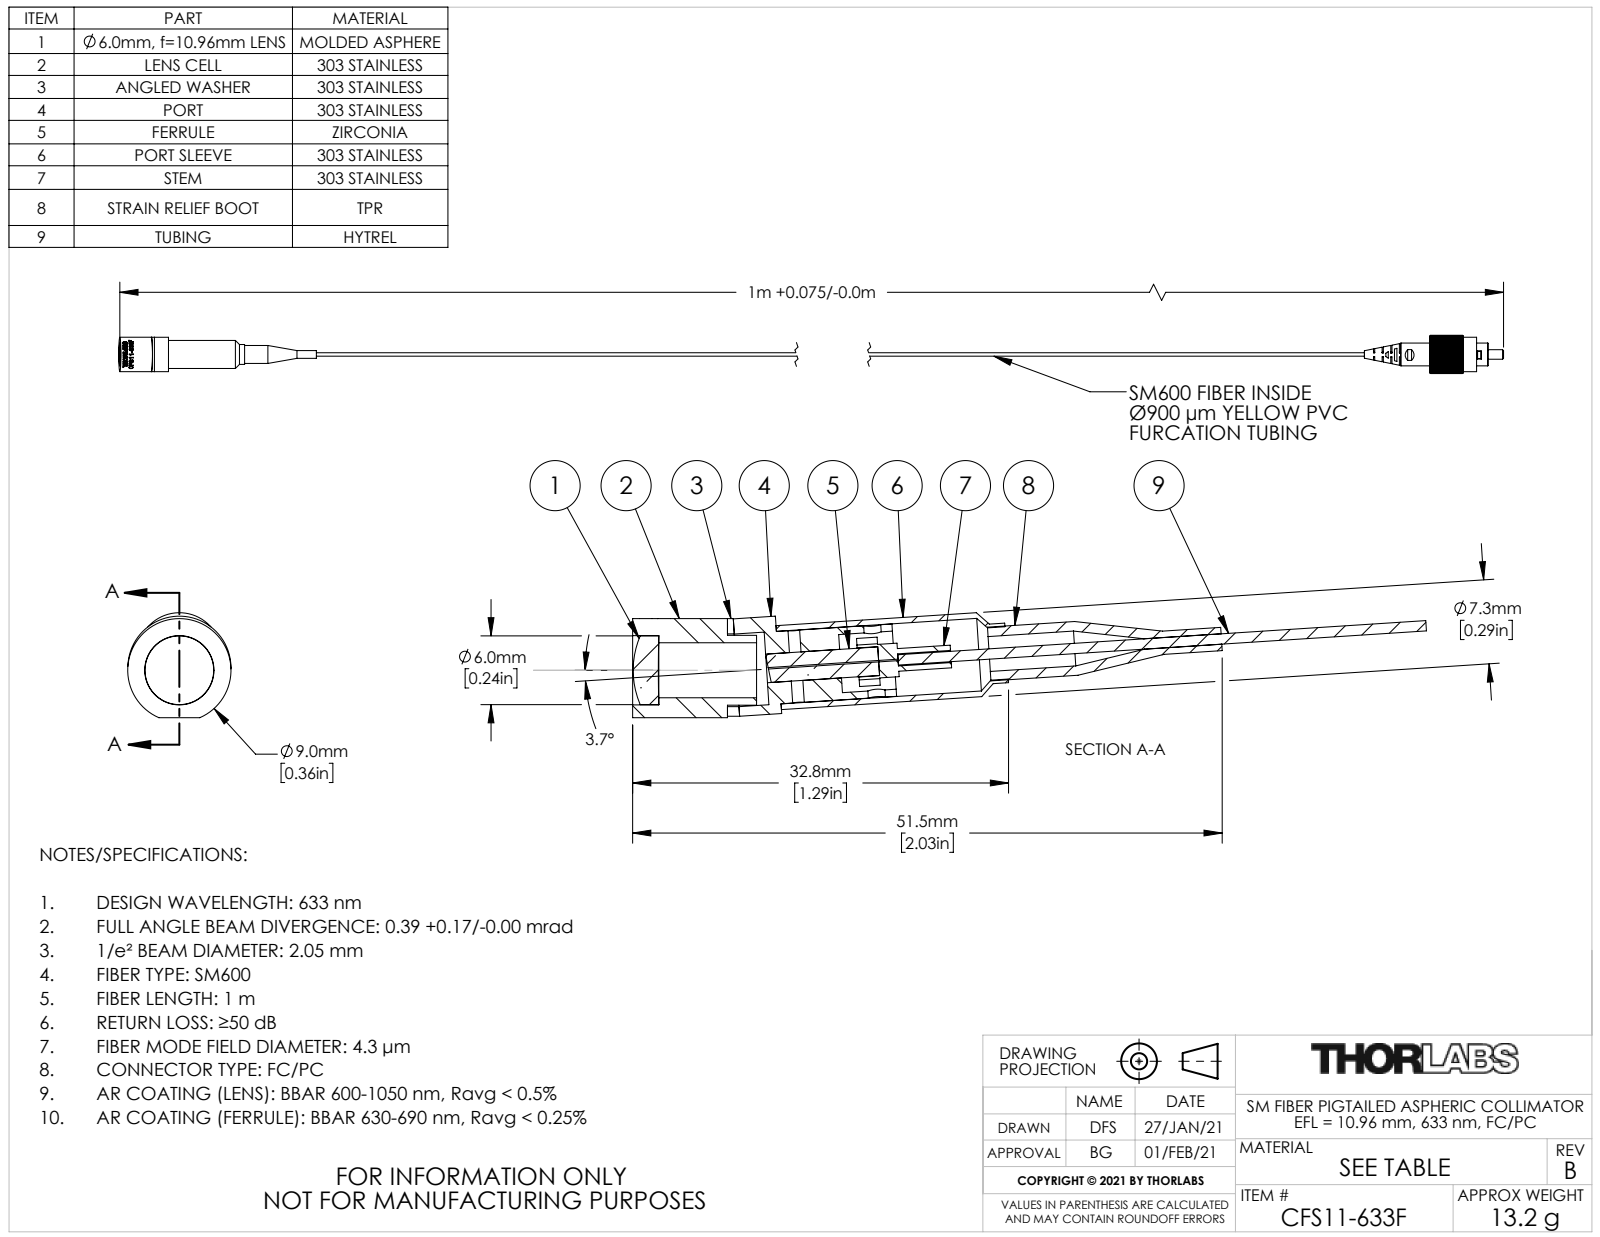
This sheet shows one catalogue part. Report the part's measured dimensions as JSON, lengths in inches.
{"part_name": "TTN155844-E0W", "step_written_by": "SolidWorks 2018 (CONFIG_CONTROL_DESIGN)", "units": "inches", "bodies": {"solids": 9, "faces": 162, "planar": 40, "cylindrical": 105, "other": 17}, "overall_size": [2.742, 0.361, 0.355], "volume_in3": 0.075, "surface_area_in2": 4.543, "round_holes": [[0.04, 2], [0.059, 2], [0.25, 2], [0.036, 1], [0.042, 1], [0.098, 1], [0.1, 1], [0.12, 1], [0.18, 1], [0.189, 1], [0.2, 1], [0.238, 1]], "round_bosses_or_shafts": [[0.355, 1], [0.354, 1], [0.289, 1], [0.249, 1], [0.24, 1], [0.236, 1], [0.205, 1], [0.185, 1]], "partial_cylinders_radius": [[0.088, 1]], "face_to_face_distances": [0.145, 0.326, 0.103, 0.042, 0.358, 0.255, 0.213, 0.489, 0.386, 0.344], "hole_center_spacings": [0.27]}
